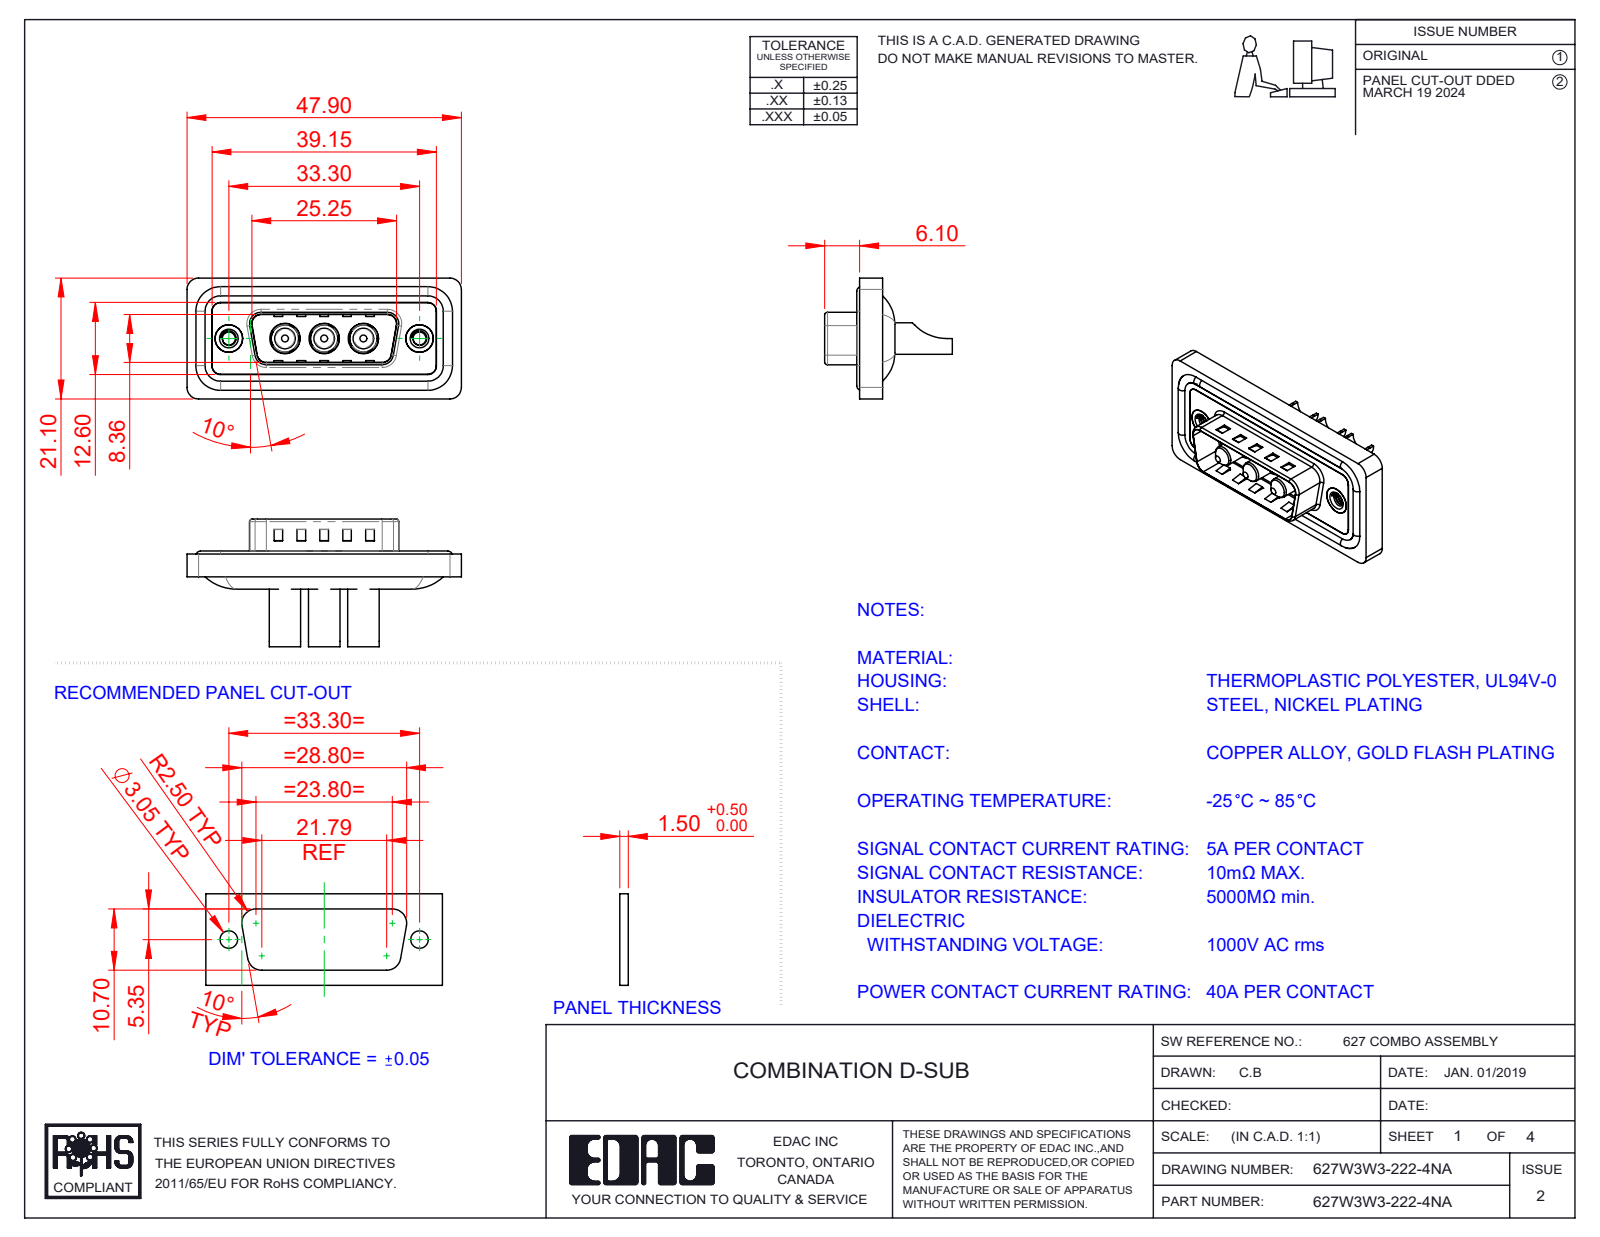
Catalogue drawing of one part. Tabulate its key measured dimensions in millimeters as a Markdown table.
| quantity | value |
| --- | --- |
| part name | 627Combo Threaded Rivet_A; Power Pin_40A SC; 627Combo Shell Front_15 Contacts; 627Combo Housing_3W3 (+3 more) |
| STEP written by | SolidWorks 2023 (CONFIG_CONTROL_DESIGN) |
| units | millimeters |
| bodies | 13 solids, 574 faces (213 planar, 246 cylindrical, 115 other) |
| overall size | 47.9 × 22.3 × 21.1 |
| volume | 5 707 mm³ |
| surface area | 9 171 mm² |
| round holes (diameter × count) | 4.6 × 3, 4.85 × 3, 5.3 × 3, 2.26 × 2, 4 × 2, 4.8 × 2, 5 × 2 |
| round bosses / shafts (diameter × count) | 1.6 × 4, 5.5 × 3, 5.2 × 3, 4.75 × 3, 3.75 × 3, 3.6 × 3, 4.9 × 2 |
| partial cylindrical surfaces (radius × count) | 1.5 × 26, 2 × 20, 0.5 × 8, 1.6 × 8, 0.25 × 4, 0.6 × 4, 0.65 × 4, 0.9 × 4 |
| main face-to-face distances | 0.4, 1.1, 0.5, 1.6, 3.1, 2.9, 1.5, 0.82, 9.58, 2.5 |
| hole center spacings | 6.85, 9.8, 16.65, 23.5, 13.7, 33.3 |
